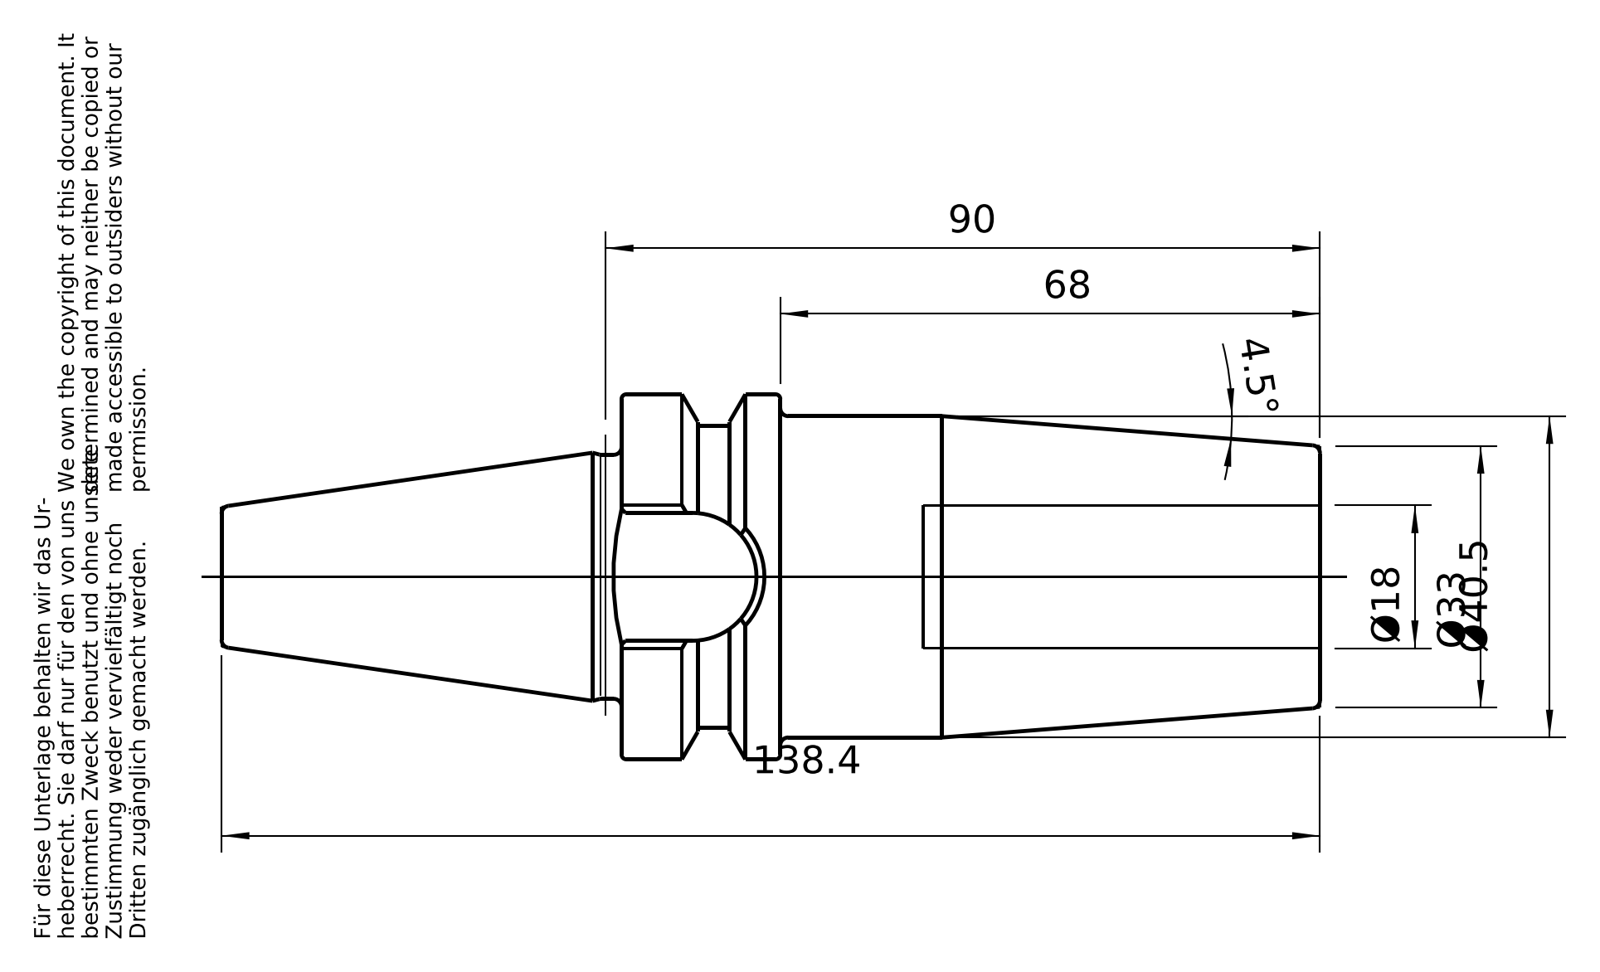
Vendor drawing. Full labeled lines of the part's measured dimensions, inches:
Part name (STEP PRODUCT): 30-640-18
STEP written by: PRO/ENGINEER BY PARAMETRIC TECHNOLOGY CORPORATION, 2010430 (CONFIG_CONTROL_DESIGN)
Units: inches
Bodies: 1 solid, 96 faces (26 planar, 22 cylindrical, 48 other)
Overall size (bounding box): 5.449 × 1.81 × 1.81
Volume: 6.94 in³ · Surface area: 34.51 in²
Round holes (diameter × count): ⌀0.398 ×1, ⌀0.493 ×1, ⌀0.512 ×1, ⌀0.709 ×1
Round bosses / shafts (diameter × count): ⌀1.81 ×1, ⌀1.594 ×1, ⌀1.211 ×1, ⌀0.473 ×1
Partial cylindrical surfaces — rounded edges, fillets, slot ends (radius × count): R0.319 ×1, R0.743 ×1
Main face-to-face distances: 3.465, 1.496, 1.969, 1.272, 0.787, 0.709, 2.677, 0.638, 1.984, 2.772
